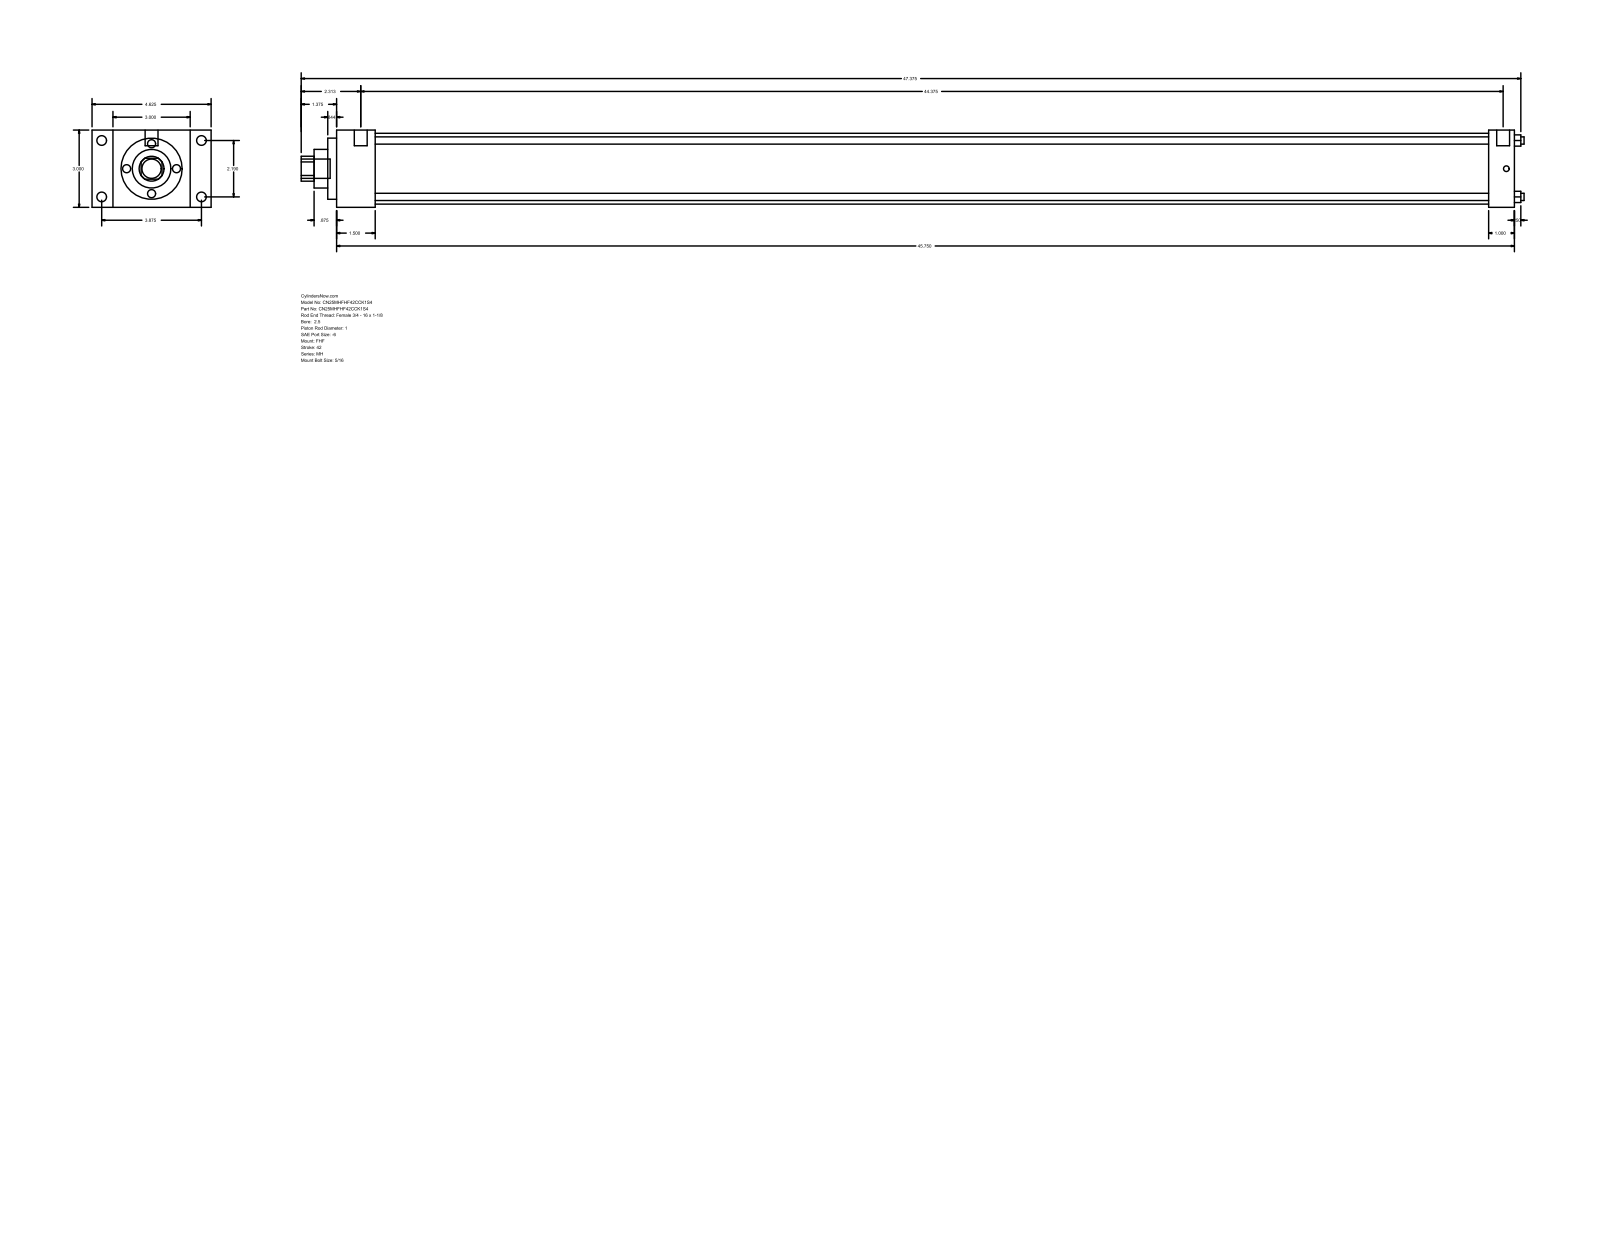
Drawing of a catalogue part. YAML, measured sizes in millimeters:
part_name: "MH_FHF__0250_1"
step_written_by: "GSSL Pune (CONFIG_CONTROL_DESIGN)"
units: millimeters
bodies: {solids: 0, faces: 90, planar: 61, cylindrical: 29, other: 0}
overall_size: [1206.5, 117.47, 76.2]
round_holes:
  - {diameter: 7.14, count: 4}
  - {diameter: 25.4, count: 1}
  - {diameter: 38.1, count: 1}
  - {diameter: 60.33, count: 1}
  - {diameter: 69.85, count: 1}
round_bosses_or_shafts:
  - {diameter: 9.53, count: 4}
  - {diameter: 5.56, count: 4}
  - {diameter: 12.7, count: 2}
  - {diameter: 19.05, count: 1}
partial_cylinders:
  - {radius: 12.29, count: 1}
face_to_face_distances: [76.2, 1162.05, 38.11, 1123.94, 20.64, 96.84, 117.48, 25.39, 1136.66, 1098.55]
hole_center_spacings: [39.33, 55.62, 78.66]
